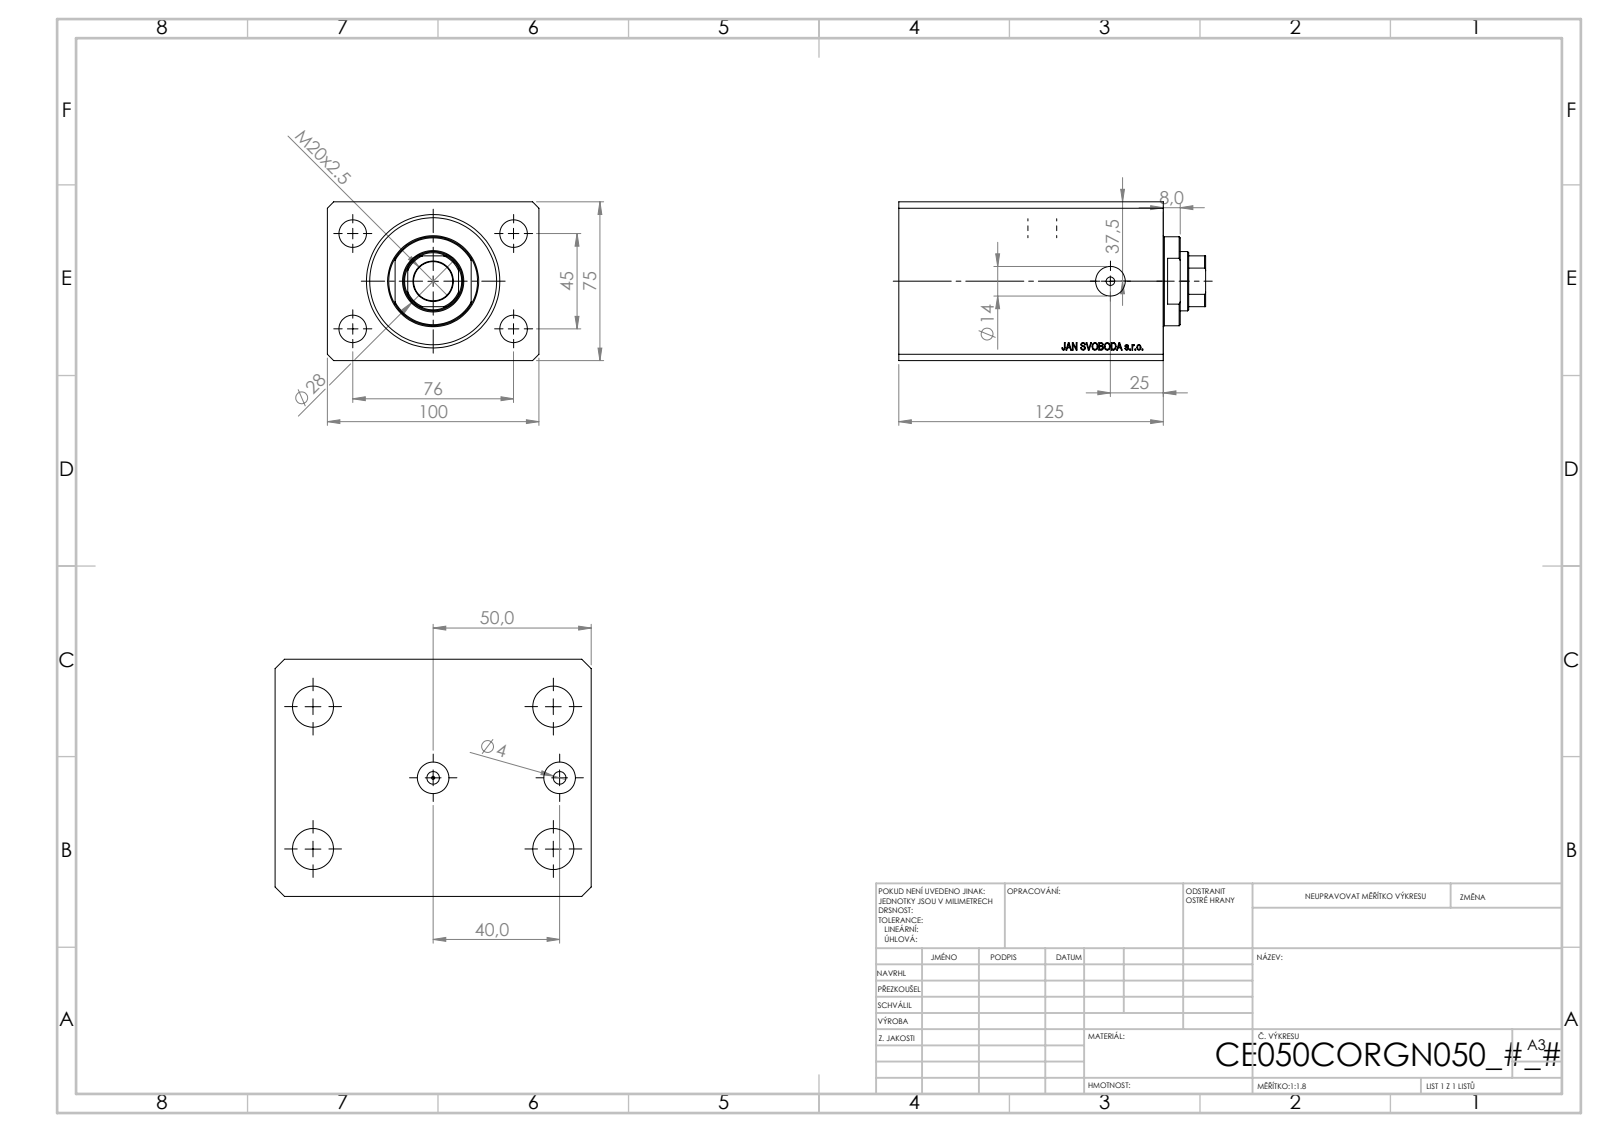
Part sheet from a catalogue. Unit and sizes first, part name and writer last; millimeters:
Units: millimetres
Overall size (bounding box): 144.9 × 100 × 75
Round holes (diameter × count): ⌀4 ×4, ⌀13 ×4, ⌀10 ×2, ⌀14 ×2, ⌀1.25 ×1, ⌀18.5 ×1, ⌀28 ×1, ⌀50 ×1, ⌀63 ×1
Round bosses / shafts (diameter × count): ⌀42 ×1
Partial cylindrical surfaces — rounded edges, fillets, slot ends (radius × count): R13.5 ×1
Main face-to-face distances: 75, 100, 125, 11.9, 113.1, 86.5, 98.4, 26.6, 48.4, 36.5
Hole centre spacings: 44.16, 22.59, 45, 76, 81.18, 88.32, 40, 75
Volume: 805 421 mm³ · Surface area: 132 888 mm²
Bodies: 3 solids, 868 faces (428 planar, 46 cylindrical, 394 other)
Part name (STEP PRODUCT): V250CE_C_Body; V250CE_C_VCP; V250CE_VC_C
STEP written by: SolidWorks 2019 (CONFIG_CONTROL_DESIGN)
